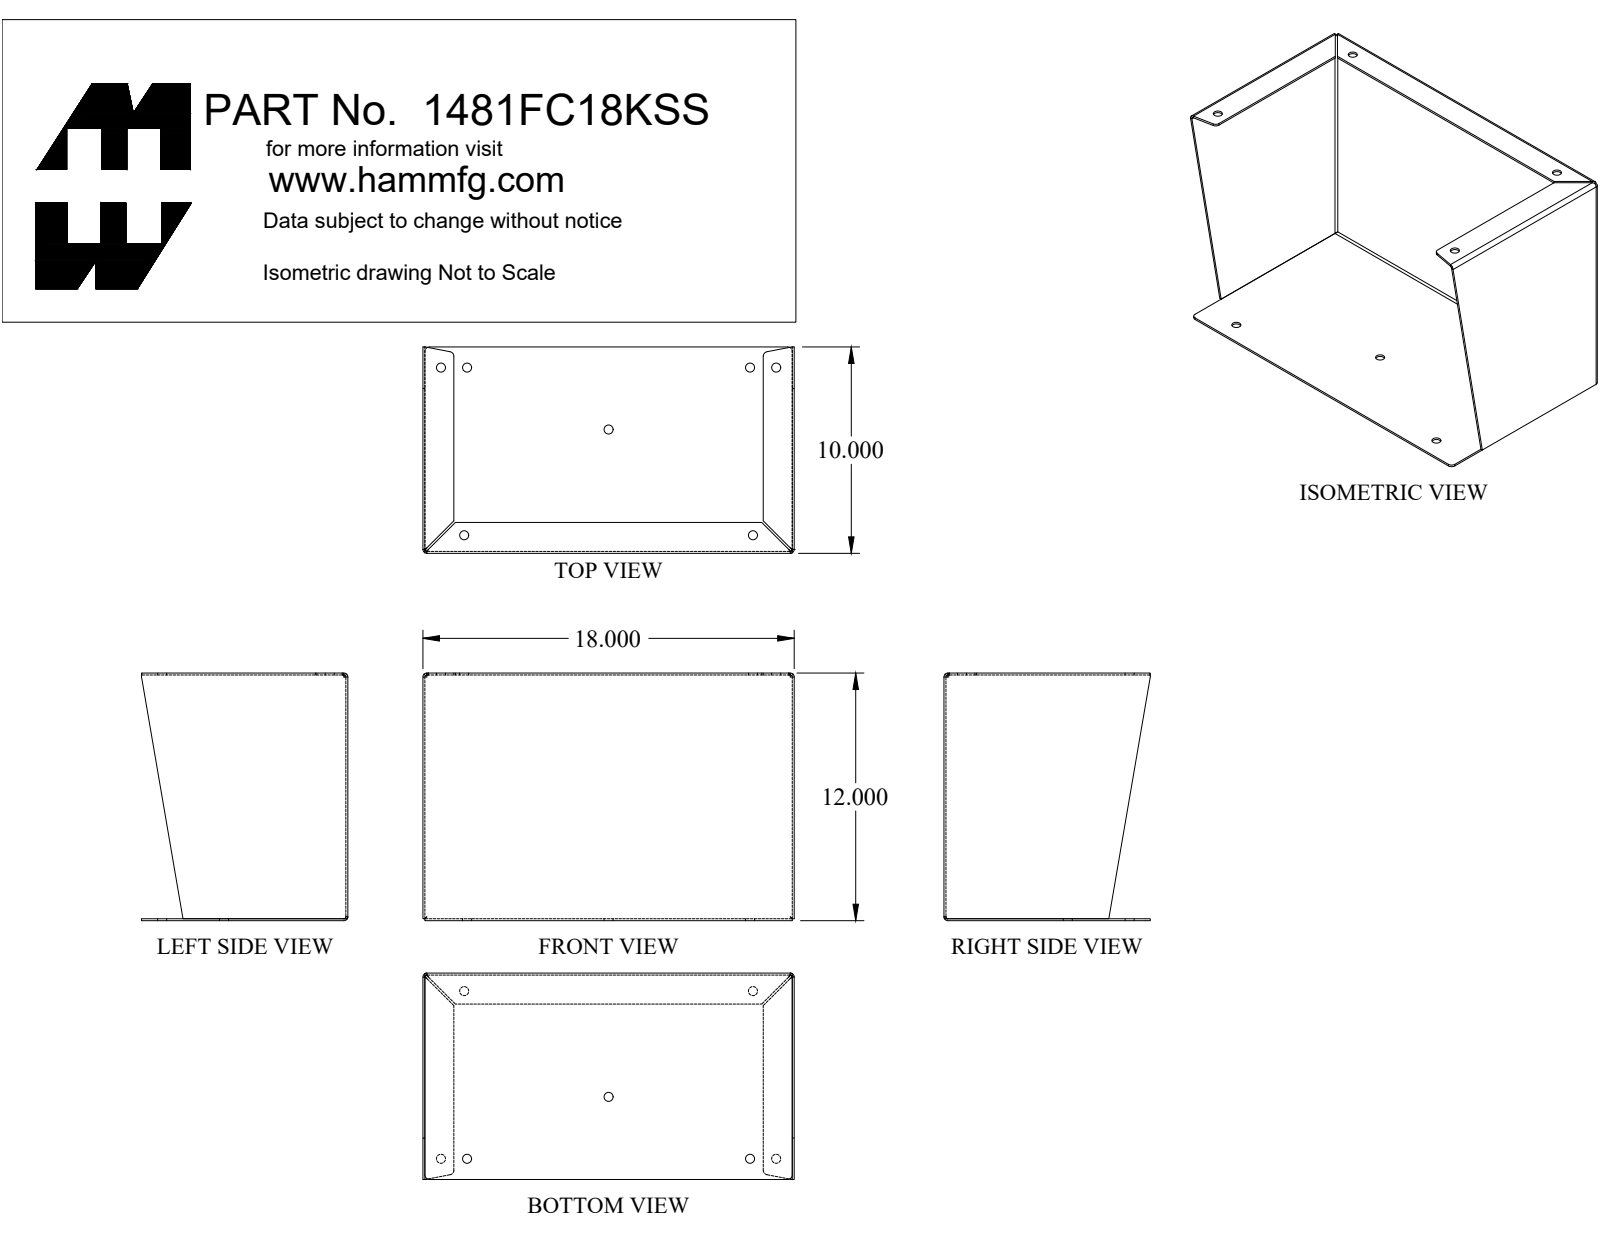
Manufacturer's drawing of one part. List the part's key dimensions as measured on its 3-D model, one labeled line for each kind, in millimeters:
Part name (STEP PRODUCT): 1481FC18KSS
STEP written by: SolidWorks 2019 (CONFIG_CONTROL_DESIGN)
Units: millimetres
Bodies: 1 solid, 71 faces (42 planar, 23 cylindrical, 6 other)
Overall size (bounding box): 457.2 × 304.8 × 254
Volume: 1 007 000 mm³ · Surface area: 842 600 mm²
Round holes (diameter × count): ⌀11.1 ×7
Partial cylindrical surfaces — rounded edges, fillets, slot ends (radius × count): R2.4 ×6, R4.8 ×6, R5.6 ×4
Main face-to-face distances: 2.4, 454.8, 2.4, 452.4, 457.2, 300, 302.4, 302.4, 304.8, 35.7
Hole centre spacings: 190.2, 206.4, 208.3, 220.4, 408.1, 32.2, 32.2, 220
